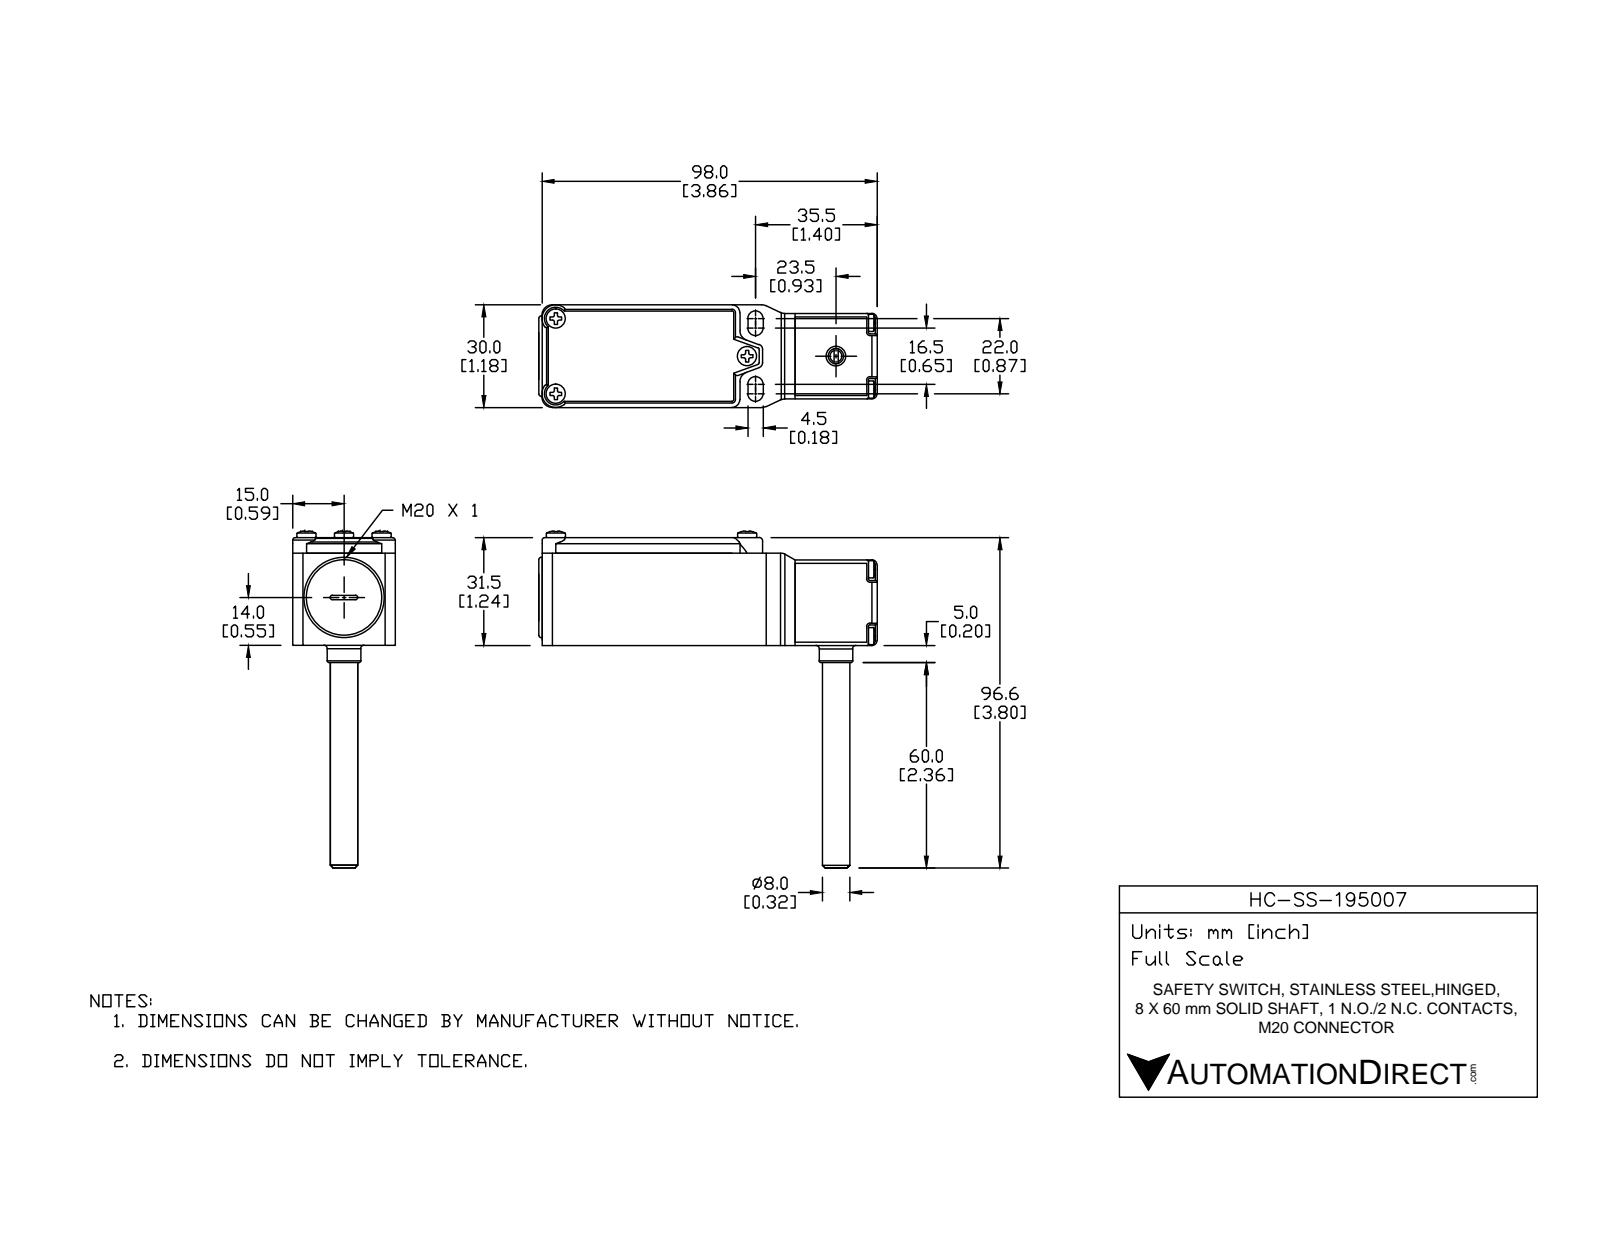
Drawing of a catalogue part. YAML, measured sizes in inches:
part_name: "HC-SS-195007"
step_written_by: "SolidWorks 2014 (AUTOMOTIVE_DESIGN)"
units: inches
bodies: {solids: 13, faces: 1168, planar: 347, cylindrical: 466, other: 355}
overall_size: [3.898, 3.876, 1.181]
volume: 2.593
surface_area: 52.81
round_holes:
  - {diameter: 0.098, count: 8}
  - {diameter: 0.126, count: 7}
  - {diameter: 0.157, count: 3}
  - {diameter: 0.059, count: 2}
  - {diameter: 0.071, count: 2}
  - {diameter: 0.087, count: 2}
  - {diameter: 0.142, count: 2}
  - {diameter: 0.081, count: 1}
  - {diameter: 0.114, count: 1}
  - {diameter: 0.173, count: 1}
  - {diameter: 0.185, count: 1}
  - {diameter: 0.217, count: 1}
round_bosses_or_shafts:
  - {diameter: 0.118, count: 7}
  - {diameter: 0.197, count: 5}
  - {diameter: 0.138, count: 4}
  - {diameter: 0.22, count: 3}
  - {diameter: 0.925, count: 1}
  - {diameter: 0.697, count: 1}
  - {diameter: 0.386, count: 1}
  - {diameter: 0.315, count: 1}
partial_cylinders:
  - {radius: 0.02, count: 175}
  - {radius: 0.039, count: 20}
  - {radius: 0.012, count: 18}
  - {radius: 0.006, count: 14}
  - {radius: 0.028, count: 8}
  - {radius: 0.118, count: 8}
  - {radius: 0.059, count: 6}
  - {radius: 0.089, count: 4}
face_to_face_distances: [0.098, 1.142, 0.079, 0.114, 1.067, 1.181, 0.177, 1.24, 0.016, 1.083]
hole_center_spacings: [0.543, 0.768, 0.187, 0.245, 0.414, 0.423, 0.426, 0.476]
